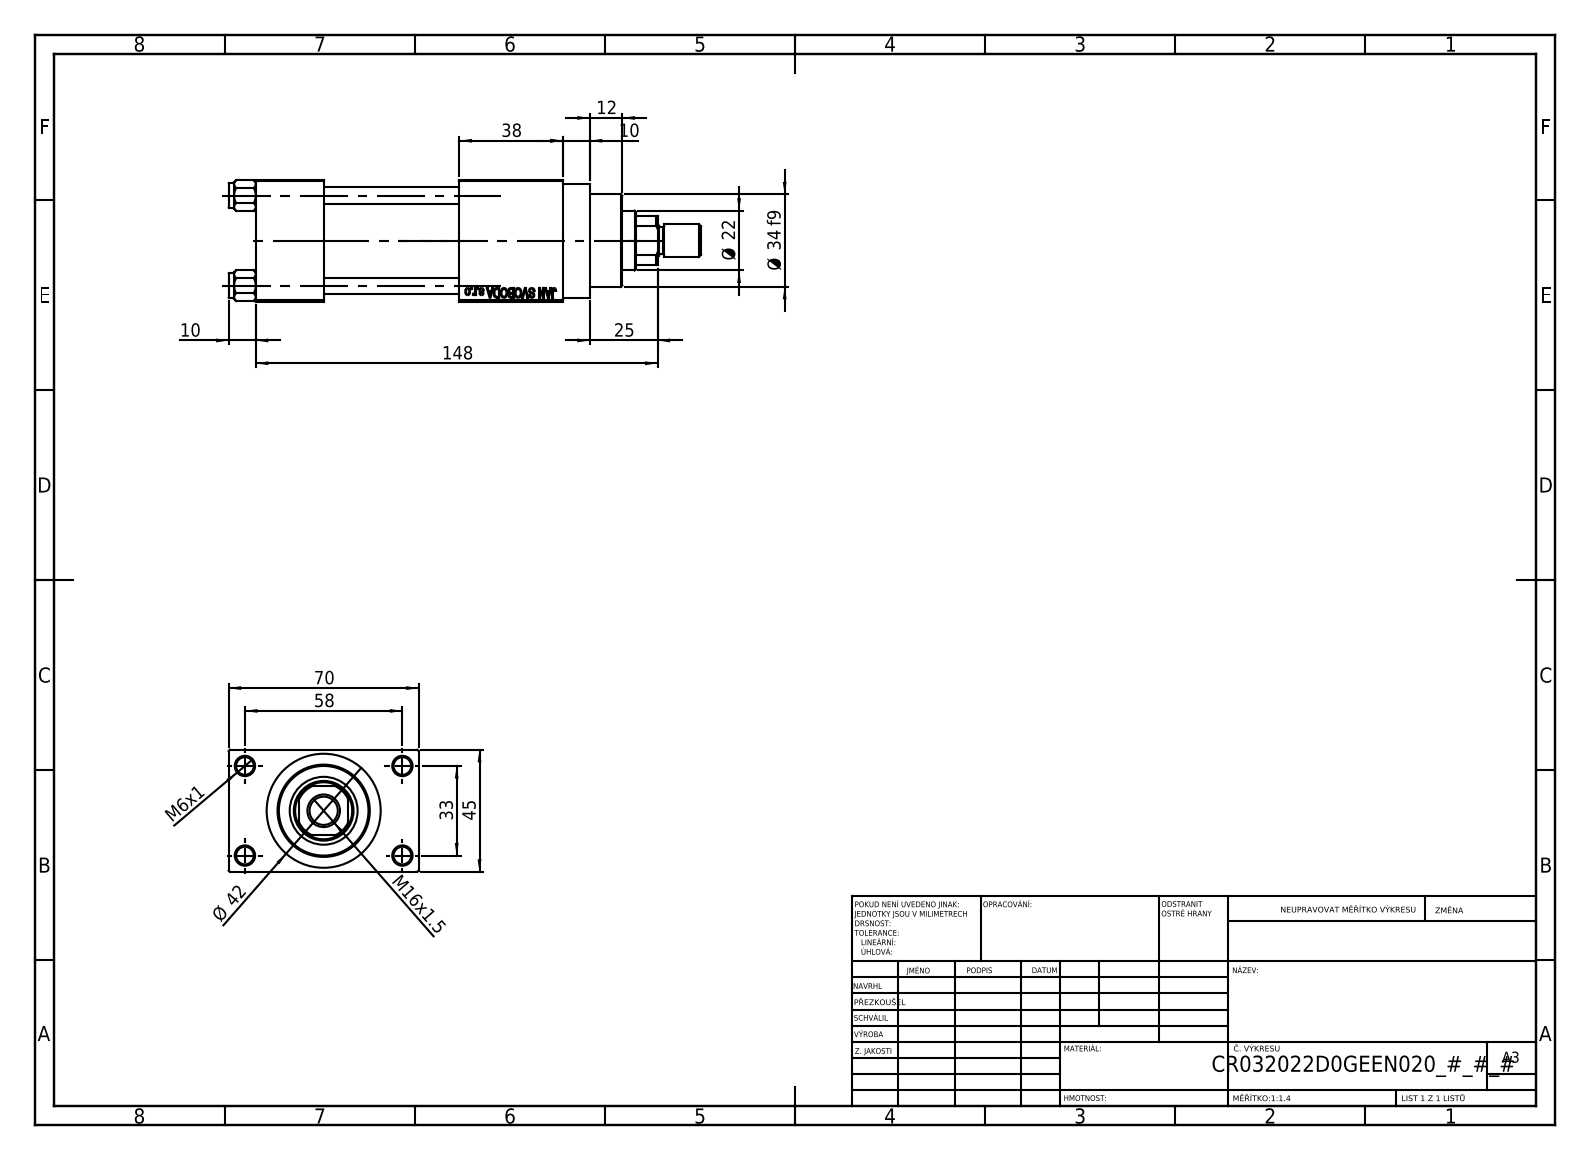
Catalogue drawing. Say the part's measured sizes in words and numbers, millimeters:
The part is named "V215CR_D_Body; NUT_M5_D; V215_VC_A; ROD_END_E (+2 more)". Its 3-D file was written by "SolidWorks 2019 (CONFIG_CONTROL_DESIGN)". It is 12 solids with 1117 faces: 500 planar, 93 cylindrical and 524 other. Overall it measures 174 by 70 by 45 millimeters. Its volume is 246 352 cubic millimeters and its surface area 80 304 square millimeters. Round holes: 4 of diameter 6, 4 of diameter 6.5, 2 of diameter 7, 2 of diameter 13.16, 2 of diameter 20, 1 of diameter 10.5, 1 of diameter 22, 1 of diameter 24, 1 of diameter 25, 1 of diameter 32, 1 of diameter 33. Round bosses or shafts: 4 of diameter 9, 1 of diameter 42, 1 of diameter 38, 1 of diameter 34, 1 of diameter 12, 1 of diameter 10. Partial cylindrical surfaces (rounded edges, fillets, slot ends): 1 of radius 10.5. The main face-to-face distances are 45, 25, 12.5, 57.5, 50, 75, 88, 70, 38, 113. The hole center spacings are 12.4, 23.48, 33.2, 33.37, 35.35, 45.6, 56.35, 33.
